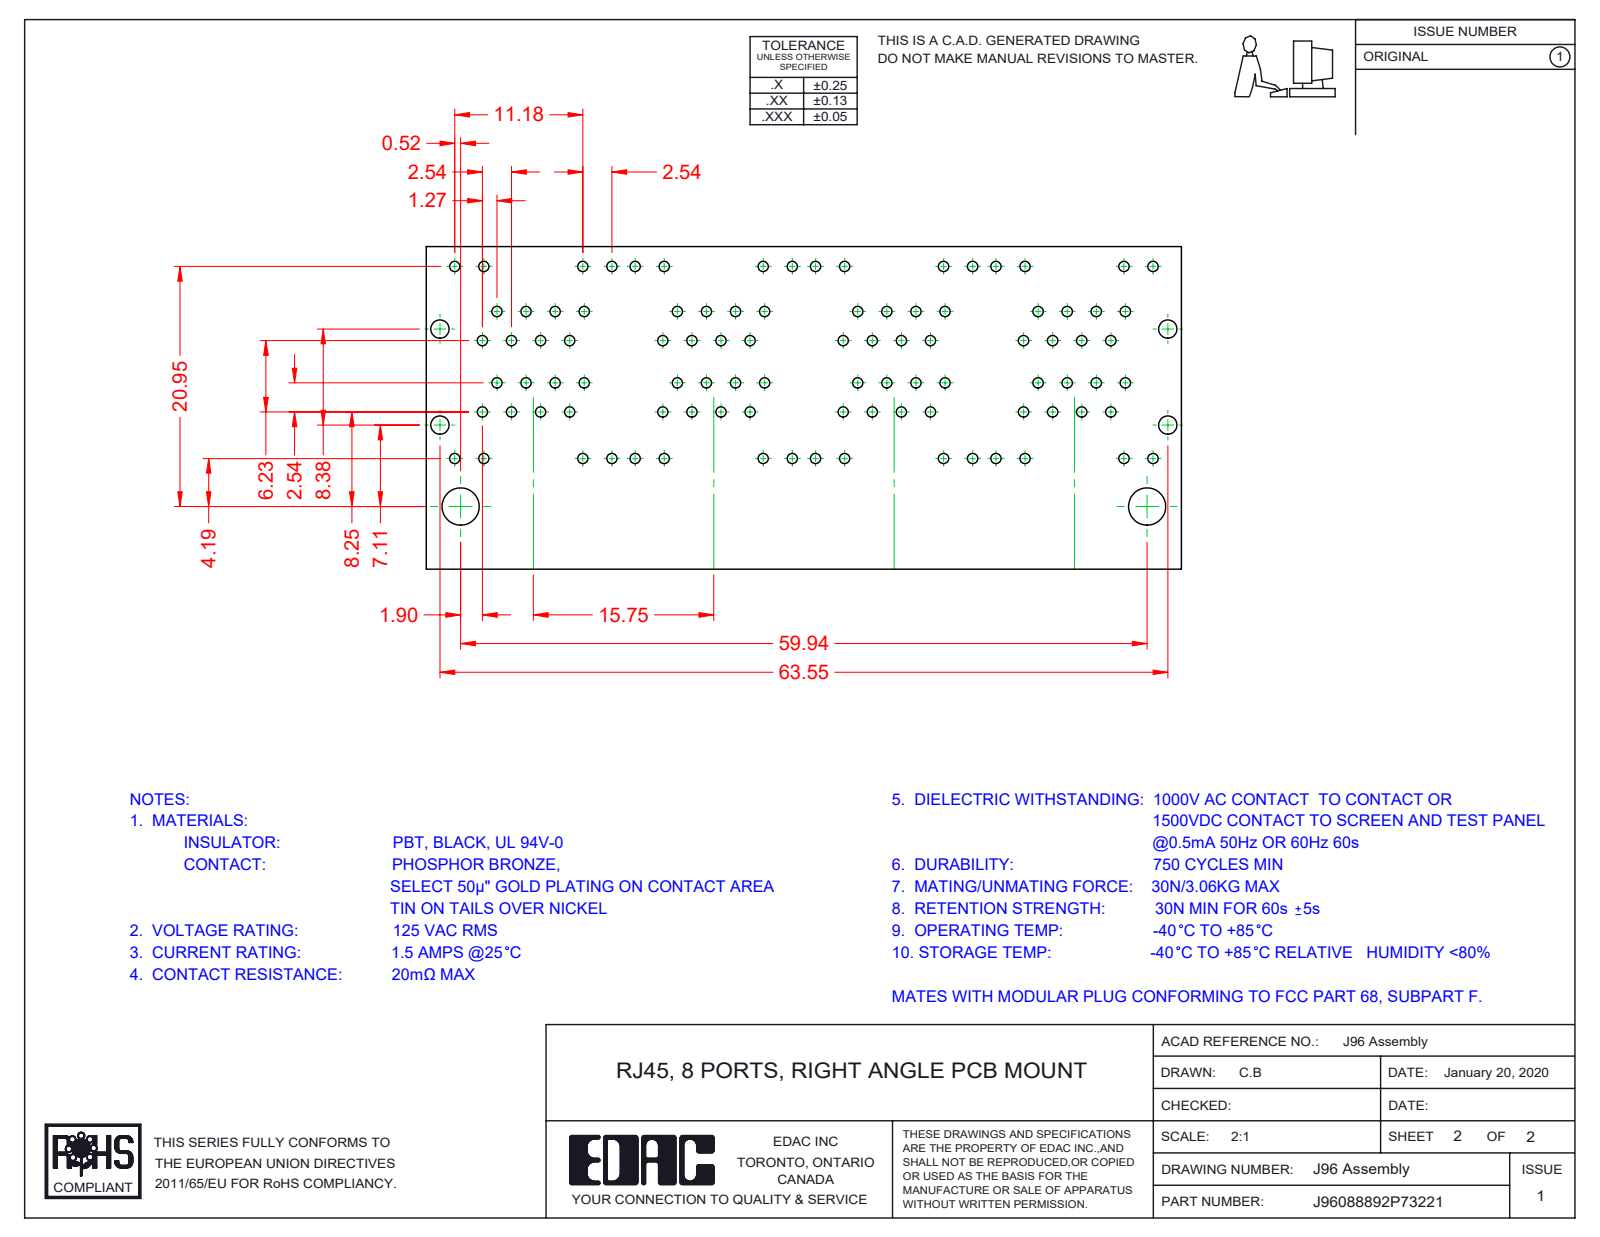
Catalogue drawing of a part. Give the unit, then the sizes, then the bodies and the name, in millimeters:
Units: millimetres
Overall size (bounding box): 67.35 × 31.38 × 28.68
Round holes (diameter × count): ⌀1.7 ×3
Round bosses / shafts (diameter × count): ⌀1.68 ×3
Partial cylindrical surfaces — rounded edges, fillets, slot ends (radius × count): R0.25 ×124, R0.35 ×73, R1 ×72, R0.5 ×49, R0.91 ×32, R0.2 ×27, R0.27 ×14, R0.7 ×11
Main face-to-face distances: 15.75, 0.35, 9.95, 1.17, 1.6, 0.54, 9.98, 10.18, 12.67, 3.37
Hole centre spacings: 15.75, 31.5
Volume: 24 149 mm³ · Surface area: 63 596 mm²
Bodies: 96 solids, 7820 faces (6105 planar, 1404 cylindrical, 311 other)
Part name (STEP PRODUCT): 96 Back Plate_8 Ports; 96 Contact Lock Upper; 96 Contacts Upper; 96 Insulator Insert (+8 more)
STEP written by: SolidWorks 2016 (CONFIG_CONTROL_DESIGN)
